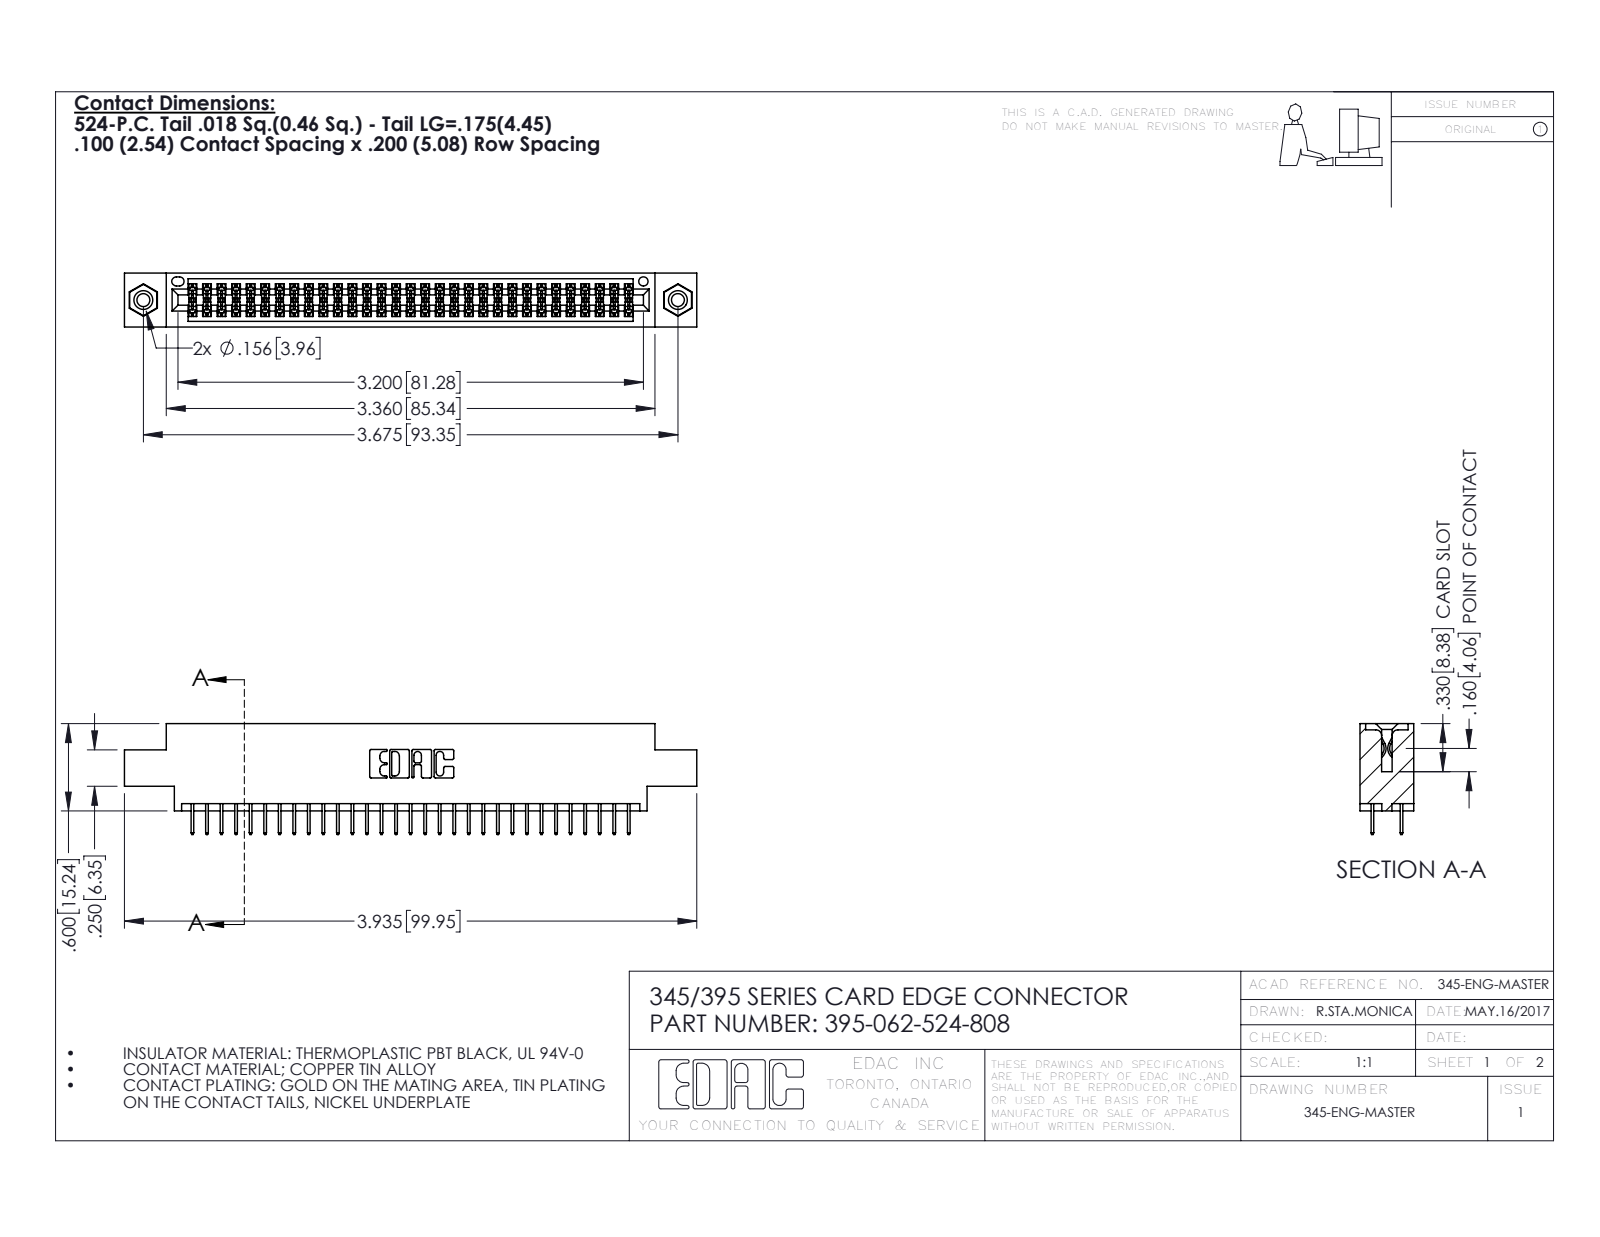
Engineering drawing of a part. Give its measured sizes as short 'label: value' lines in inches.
name: 345 Part_0.170 Offset - 0.156 Dia-TI; 345-292-001_345-293-124; 345-250-001_345-250-003-102; 395-062-524-808
written by: SolidWorks 2016 (CONFIG_CONTROL_DESIGN)
unit: in
bodies: 65 solids, 3538 faces (2534 planar, 988 cylindrical, 16 other)
size: 3.935 × 0.762 × 0.37
volume: 0.573 in³; area: 21.05 in²
holes: 2× ⌀0.089, 2× ⌀0.125, 2× ⌀0.156, 1× ⌀0.064
bosses: 2× ⌀0.155
rounds: 93× R0.006, 22× R0.01, 6× R0.007, 6× R0.031, 3× R0.026, 2× R0.014, 2× R0.019, 2× R0.022
face distances: 0.072, 0.298, 0.37, 0.2, 0.098, 0.272, 0.025, 0.225, 0.175, 0.072
hole spacings: 0.27, 3.44, 3.675
